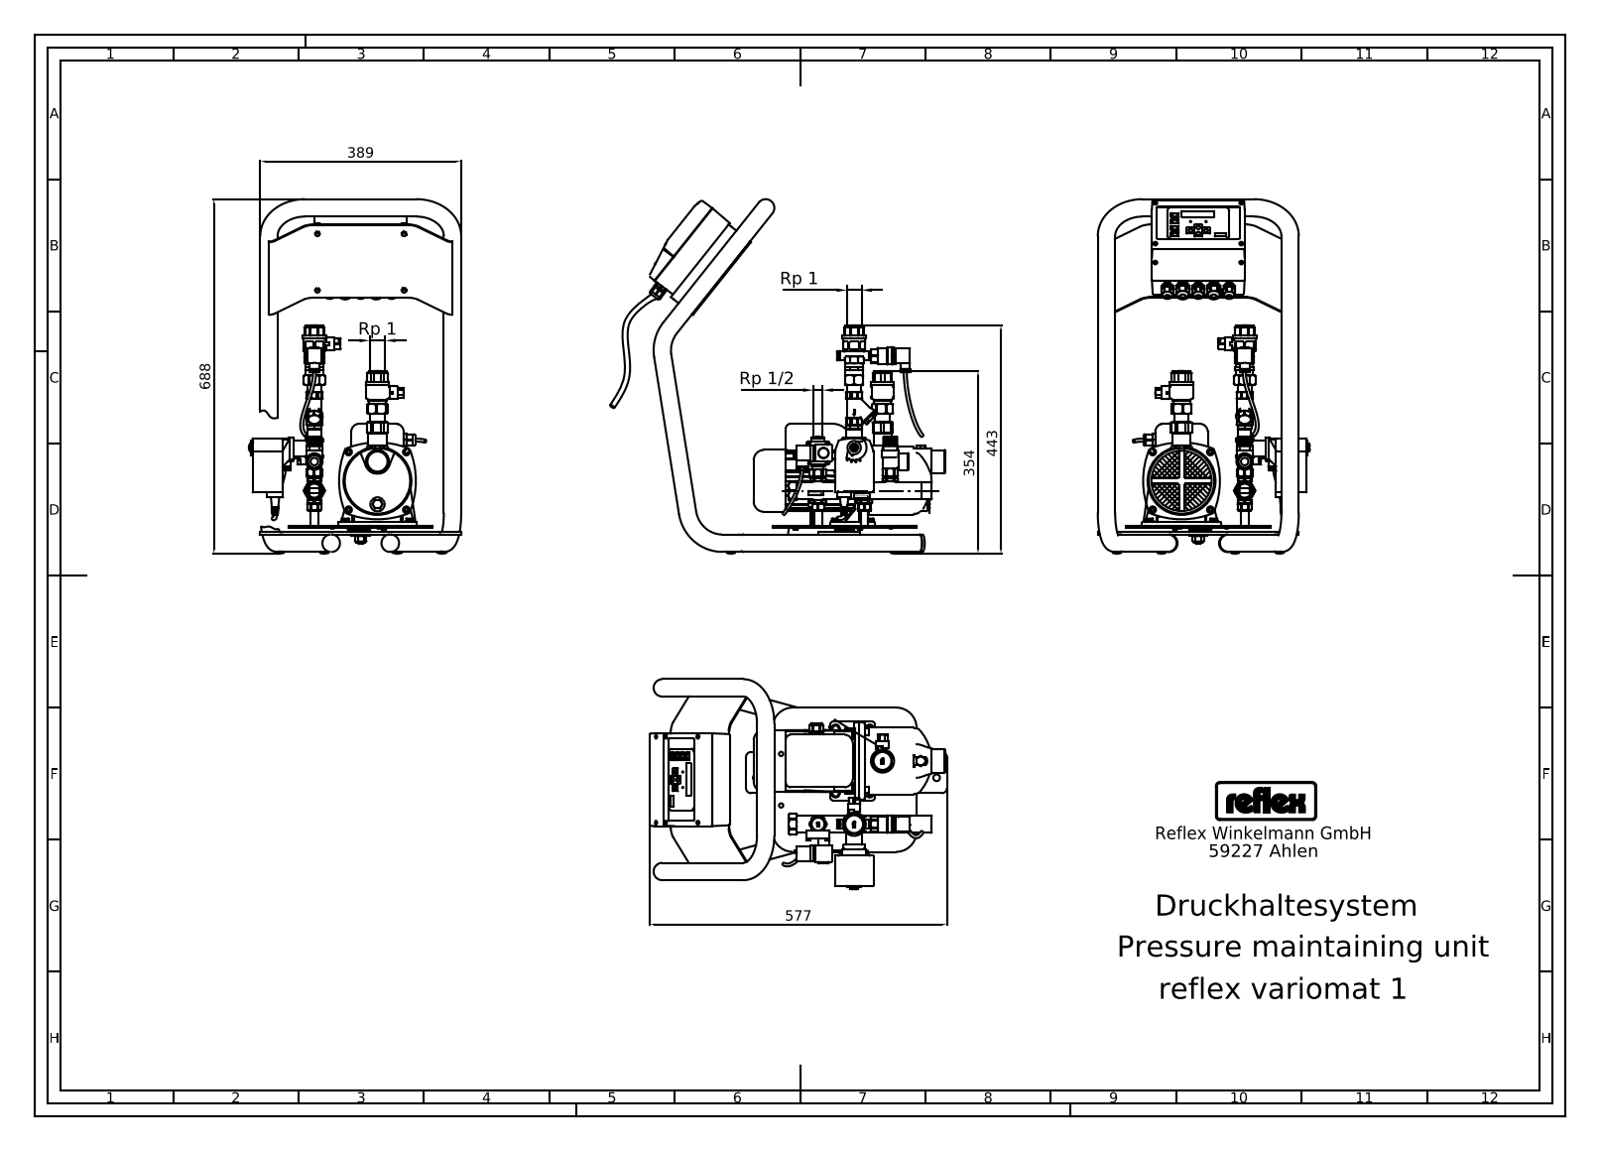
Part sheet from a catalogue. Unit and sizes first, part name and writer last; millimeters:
Units: millimetres
Overall size (bounding box): 694.2 × 576.84 × 436
Round holes (diameter × count): ⌀10.5 ×1, ⌀27 ×1, ⌀30.29 ×1, ⌀38.95 ×1
Round bosses / shafts (diameter × count): ⌀8 ×12, ⌀20 ×6, ⌀20.6 ×5, ⌀19 ×5, ⌀33.7 ×4, ⌀26 ×4, ⌀11.63 ×4, ⌀33.2 ×3
Partial cylindrical surfaces — rounded edges, fillets, slot ends (radius × count): R2 ×48, R5 ×27, R1 ×11, R105 ×10, R3 ×6, R103.2 ×5, R106.8 ×5, R4.5 ×4
Main face-to-face distances: 2, 4, 6, 10, 16, 12, 7.5, 17.5, 105.5, 113.5
Hole centre spacings: 313.06
Volume: 13 040 000 mm³ · Surface area: 1 517 000 mm²
Bodies: 55 solids, 1699 faces (1008 planar, 448 cylindrical, 243 other)
STEP written by: Mechanical Desktop 2008 (CONFIG_CONTROL_DESIGN)
